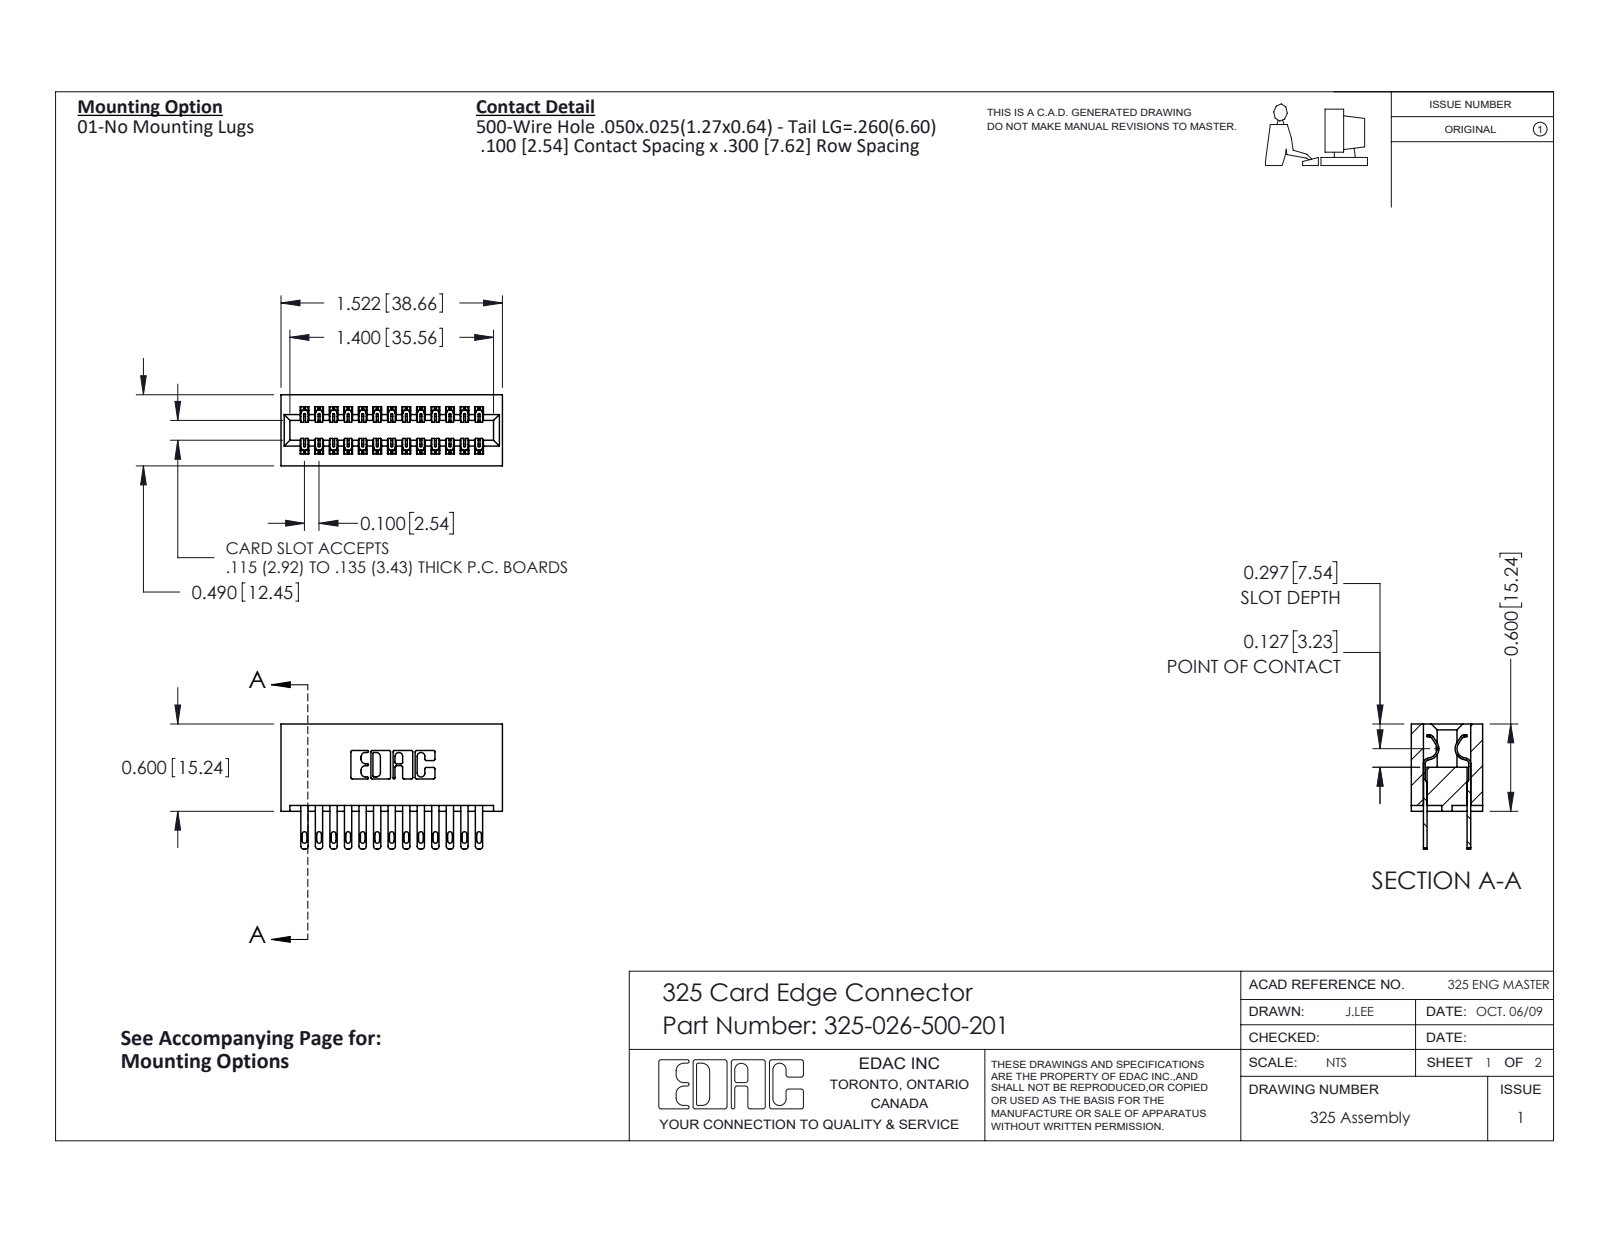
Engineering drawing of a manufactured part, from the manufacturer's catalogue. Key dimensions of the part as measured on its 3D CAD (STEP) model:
Part name (STEP PRODUCT): 325-292-001_325-293-100; 325 Part_Lugless; 325-026-500-201
STEP written by: SolidWorks 2016 (CONFIG_CONTROL_DESIGN)
Units: inches
Bodies: 27 solids, 1354 faces (846 planar, 508 cylindrical, 0 other)
Overall size (bounding box): 1.522 × 0.86 × 0.49
Volume: 0.331 in³ · Surface area: 10.54 in²
Partial cylindrical surfaces — rounded edges, fillets, slot ends (radius × count): R0.006 ×39, R0.016 ×26, R0.02 ×26, R0.01 ×22, R0.007 ×6, R0.031 ×6, R0.026 ×3, R0.014 ×2
Main face-to-face distances: 0.083, 0.407, 0.3, 0.107, 0.383, 0.025, 0.1, 0.49, 0.325, 0.2
